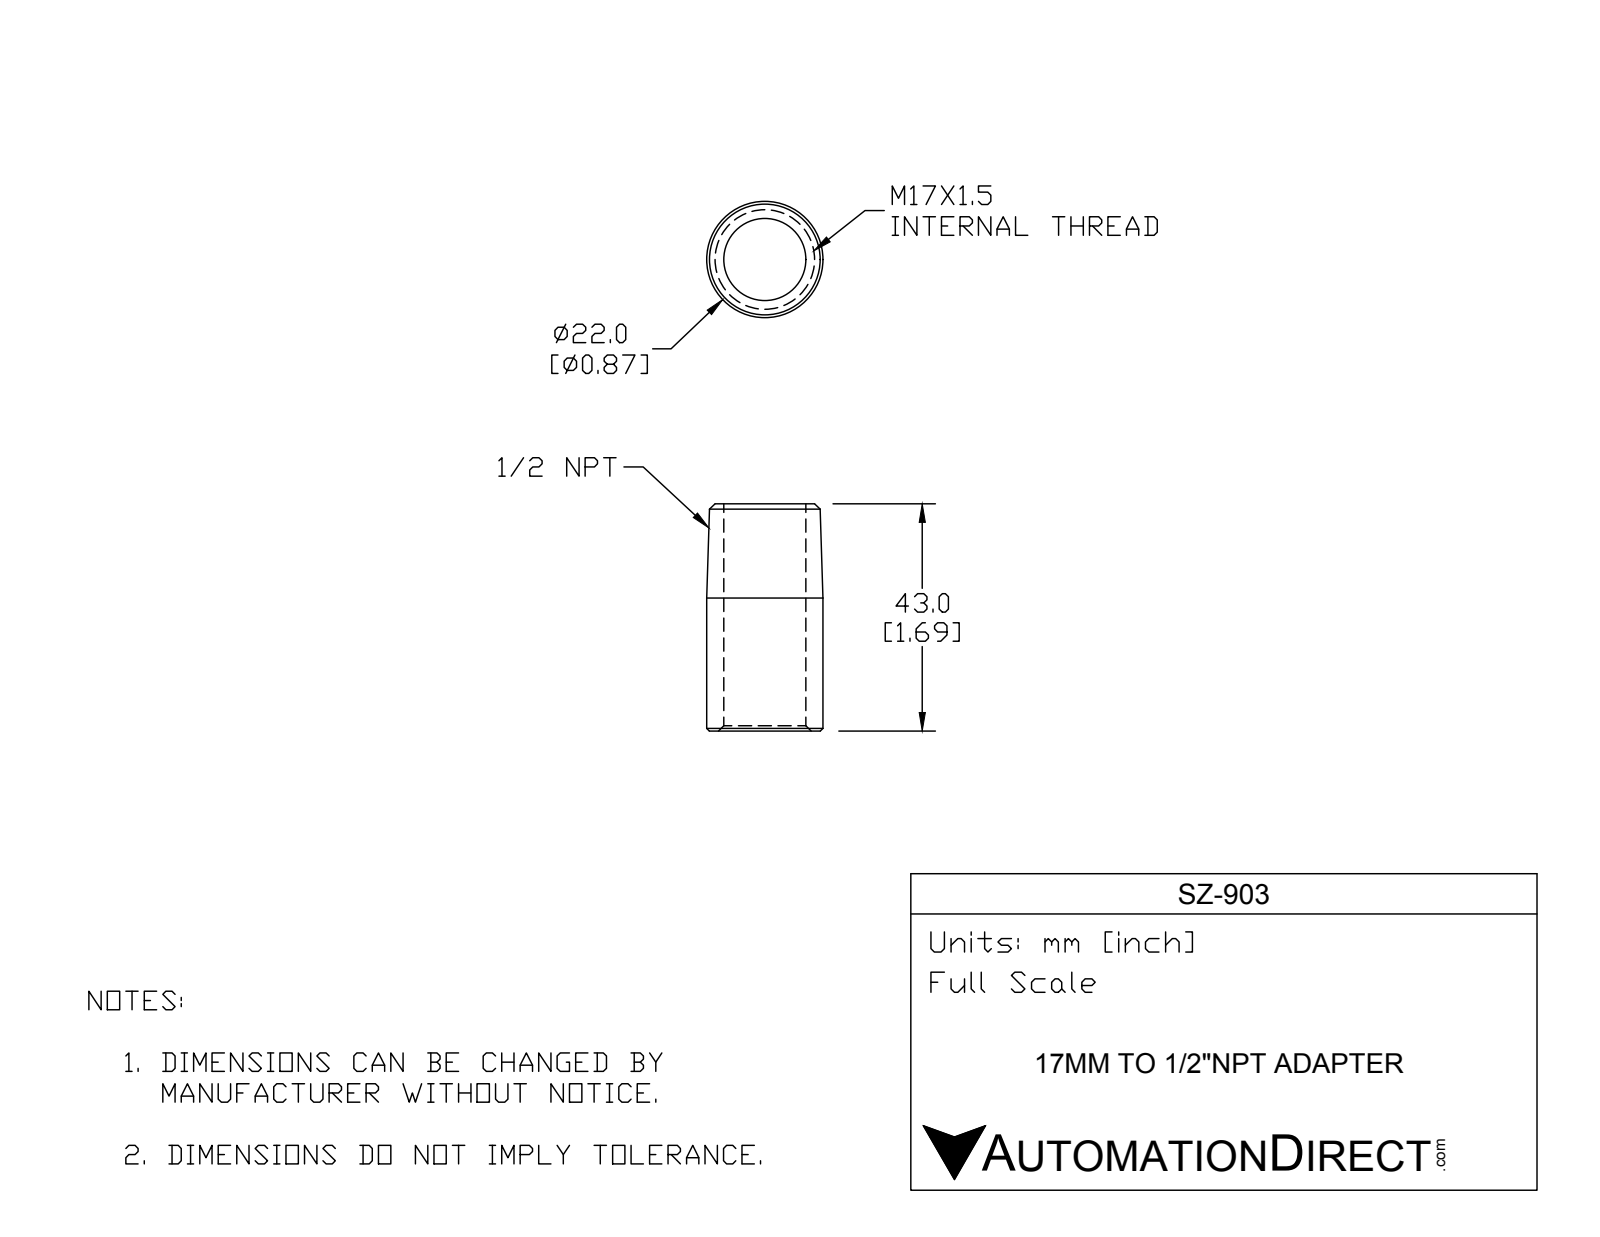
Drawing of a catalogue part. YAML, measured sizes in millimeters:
part_name: "SZ-903"
step_written_by: "SolidWorks 2016 (AUTOMOTIVE_DESIGN)"
units: millimeters
bodies: {solids: 1, faces: 14, planar: 2, cylindrical: 4, other: 8}
overall_size: [43, 22, 22]
volume: 7779
surface_area: 5299
round_holes:
  - {diameter: 15.55, count: 1}
round_bosses_or_shafts:
  - {diameter: 22, count: 1}
face_to_face_distances: [43]
